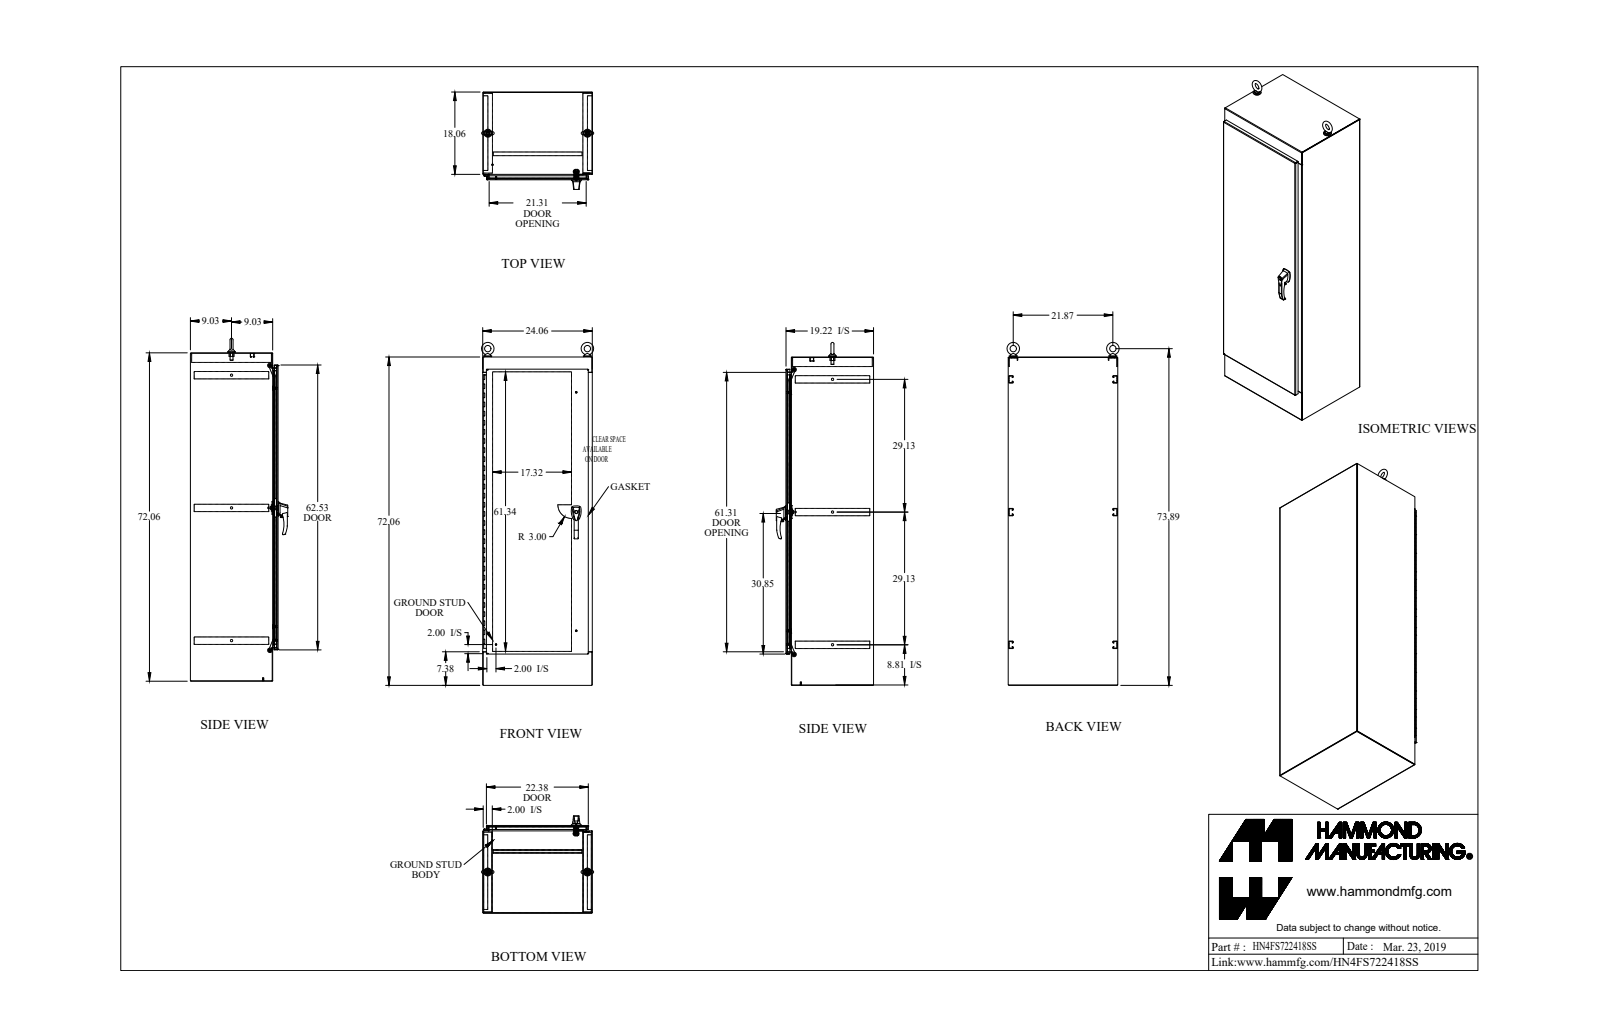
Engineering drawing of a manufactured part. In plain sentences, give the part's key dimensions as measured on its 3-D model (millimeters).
The part is named "HN4FS722418SS". Its 3-D file was written by "SolidWorks 2018 (AUTOMOTIVE_DESIGN)". It is 52 solids with 1857 faces: 854 planar, 838 cylindrical and 165 other. Overall it measures 1911.5 by 624.9 by 542.6 millimeters. Its volume is 13 500 000 cubic millimeters and its surface area 11 140 000 square millimeters. Round holes: 10 of diameter 7.7, 7 of diameter 8.9, 3 of diameter 12.7, 2 of diameter 6.4, 2 of diameter 6.5, 2 of diameter 7.1, 2 of diameter 7.1, 2 of diameter 8, 2 of diameter 9.9, 2 of diameter 10.5, 2 of diameter 13.4, 2 of diameter 15.9. Round bosses or shafts: 2 of diameter 44.5, 2 of diameter 38.1, 2 of diameter 31.8, 2 of diameter 25.4, 2 of diameter 19.1, 2 of diameter 18.7, 2 of diameter 16, 2 of diameter 15.9. Partial cylindrical surfaces (rounded edges, fillets, slot ends): 42 of radius 1.1, 36 of radius 3.5, 23 of radius 12.7, 22 of radius 3.2, 16 of radius 0.4, 15 of radius 1.2, 15 of radius 1.5, 15 of radius 3.6. The main face-to-face distances are 2.4, 486.5, 608.7, 606.3, 484, 488.9, 611.1, 1827.9, 456.3, 30.1. The hole center spacings are 152.4, 304.8, 457.2, 609.6, 762, 914.4, 1066.8, 0.4.
